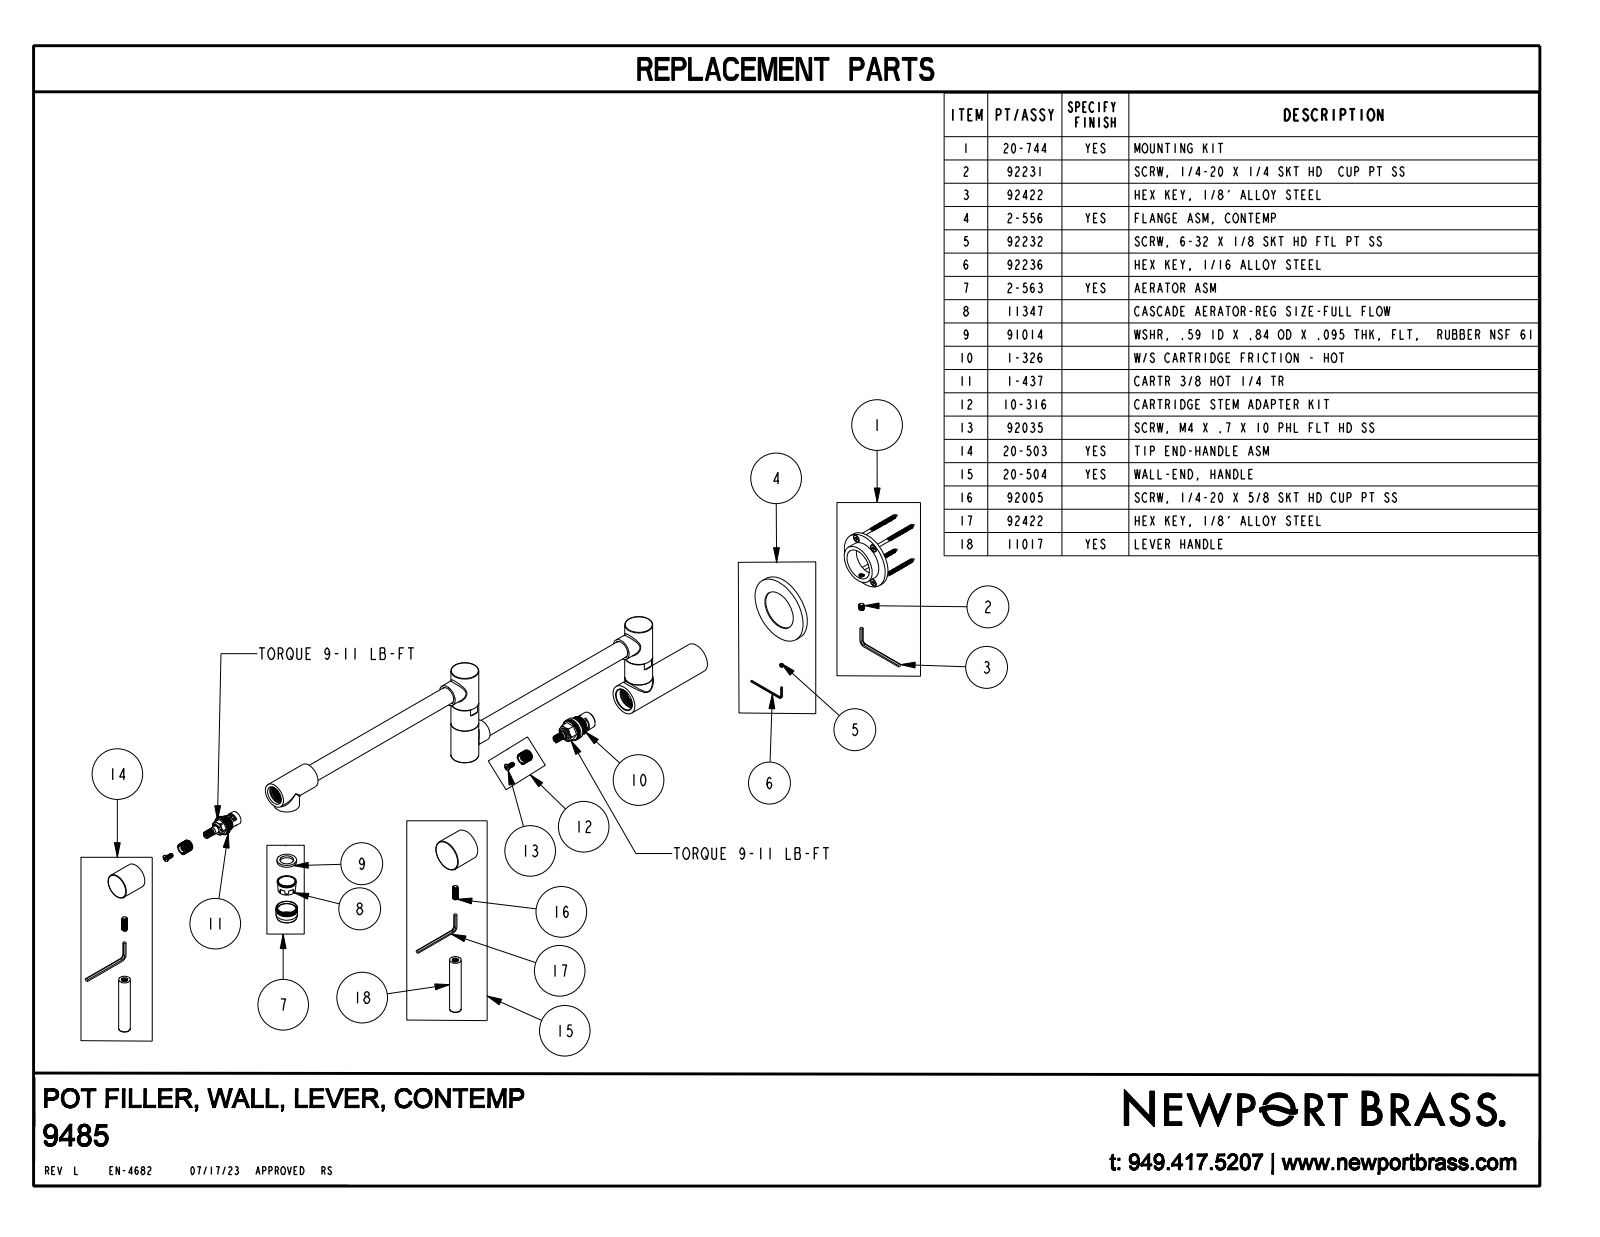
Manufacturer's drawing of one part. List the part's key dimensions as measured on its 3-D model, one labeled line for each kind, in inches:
Part name (STEP PRODUCT): 9485
STEP written by: CREO PARAMETRIC BY PTC INC, 2018400 (CONFIG_CONTROL_DESIGN)
Units: inches
Bodies: 1 solid, 112 faces (33 planar, 49 cylindrical, 30 other)
Overall size (bounding box): 26.84 × 9.496 × 2.92
Volume: 30.96 in³ · Surface area: 138.6 in²
Round bosses / shafts (diameter × count): ⌀0.94 ×4, ⌀1.2 ×2, ⌀1.1 ×2, ⌀0.75 ×2, ⌀0.5 ×2, ⌀2.92 ×1, ⌀1.7 ×1, ⌀1.35 ×1
Main face-to-face distances: 0.25, 2.86, 0.02, 5.66, 5.41, 1.576, 4.437, 0.6, 0.35, 5.06
